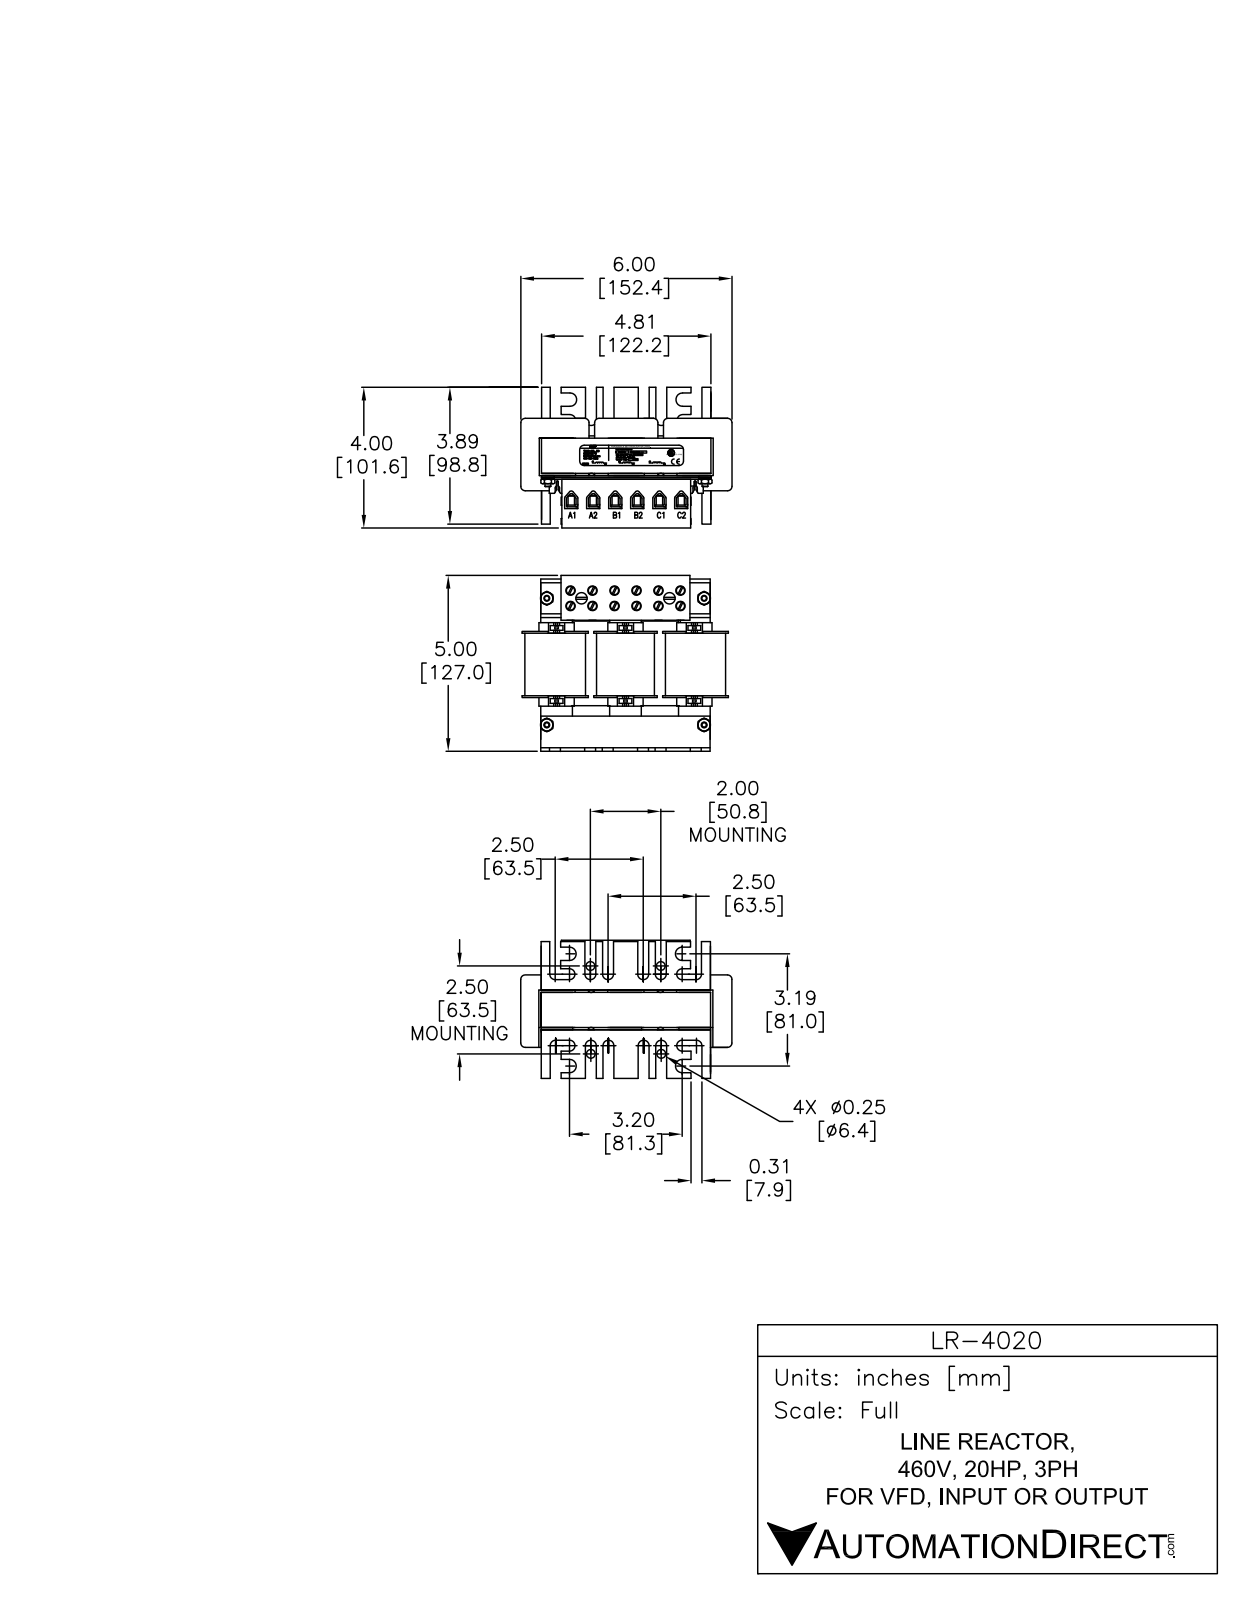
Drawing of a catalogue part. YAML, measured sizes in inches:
part_name: "LR-4020"
step_written_by: "SolidWorks 2011 (AUTOMOTIVE_DESIGN)"
units: inches
bodies: {solids: 43, faces: 1048, planar: 794, cylindrical: 222, other: 32}
overall_size: [5.699, 5.165, 3.873]
volume: 33.01
surface_area: 259
round_holes:
  - {diameter: 0.276, count: 12}
  - {diameter: 0.305, count: 5}
round_bosses_or_shafts:
  - {diameter: 0.276, count: 12}
  - {diameter: 0.404, count: 4}
  - {diameter: 0.315, count: 4}
  - {diameter: 0.305, count: 2}
  - {diameter: 0.295, count: 2}
  - {diameter: 0.134, count: 2}
  - {diameter: 0.128, count: 2}
partial_cylinders:
  - {radius: 0.155, count: 16}
  - {radius: 0.072, count: 12}
  - {radius: 0.106, count: 12}
  - {radius: 0.107, count: 12}
  - {radius: 0.197, count: 12}
  - {radius: 0.236, count: 12}
  - {radius: 0.19, count: 4}
  - {radius: 0.034, count: 3}
face_to_face_distances: [0.098, 1.073, 0.059, 1.23, 0.221, 1.373, 1.132, 1.354, 0.28, 1.294]
hole_center_spacings: [0.63, 1.26, 0.837, 1.375, 1.89, 0.551, 1.969, 0.407]
